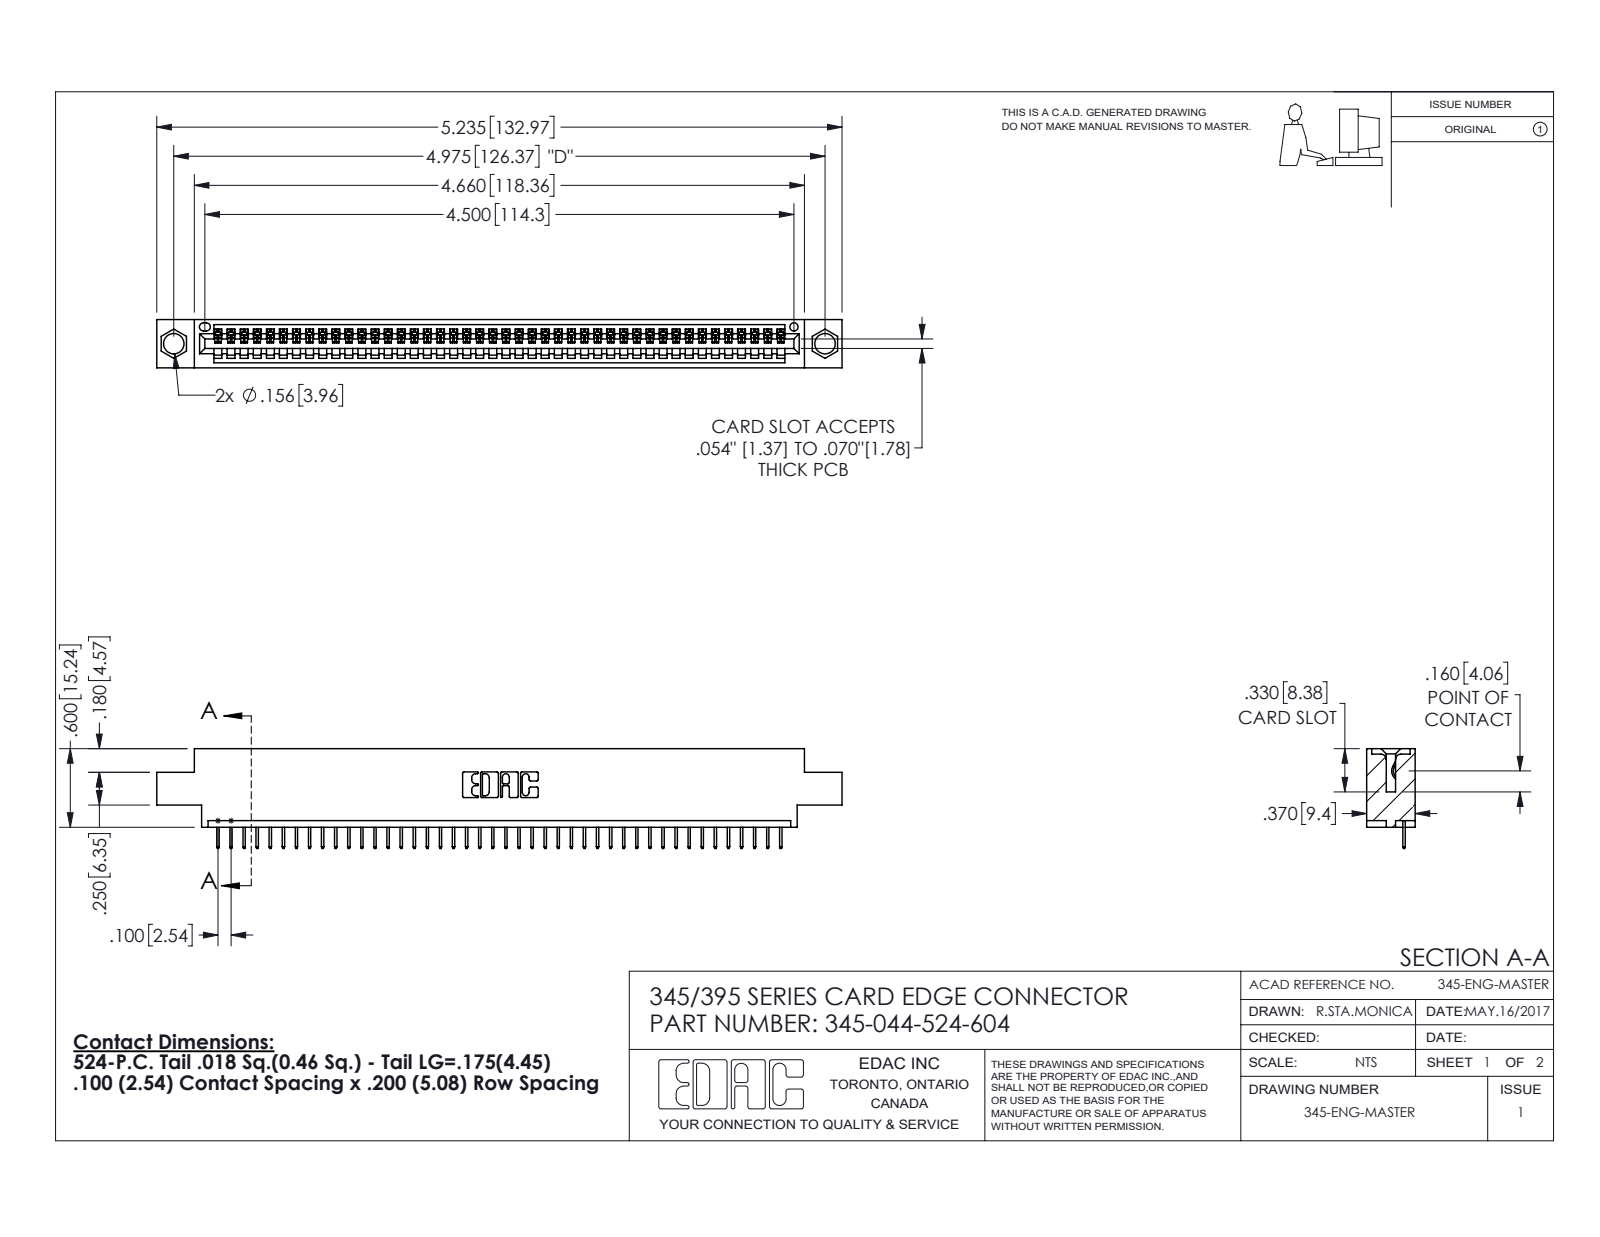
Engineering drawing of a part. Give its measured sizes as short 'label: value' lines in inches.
name: 345 Part_0.170 Offset - 0.156 Dia-TH; 345-044-524-604; 345-292-001_345-293-124
written by: SolidWorks 2016 (CONFIG_CONTROL_DESIGN)
unit: in
bodies: 45 solids, 2858 faces (2108 planar, 750 cylindrical, 0 other)
size: 5.235 × 0.762 × 0.37
volume: 0.749 in³; area: 24.36 in²
holes: 2× ⌀0.156, 1× ⌀0.064
rounds: 88× R0.006, 22× R0.01, 6× R0.007, 6× R0.031, 3× R0.026, 2× R0.031, 2× R0.04, 1× R0.014
face distances: 0.072, 0.298, 0.37, 0.2, 0.098, 0.272, 0.025, 0.225, 0.072, 0.175
hole spacings: 0.27, 4.739, 4.975
